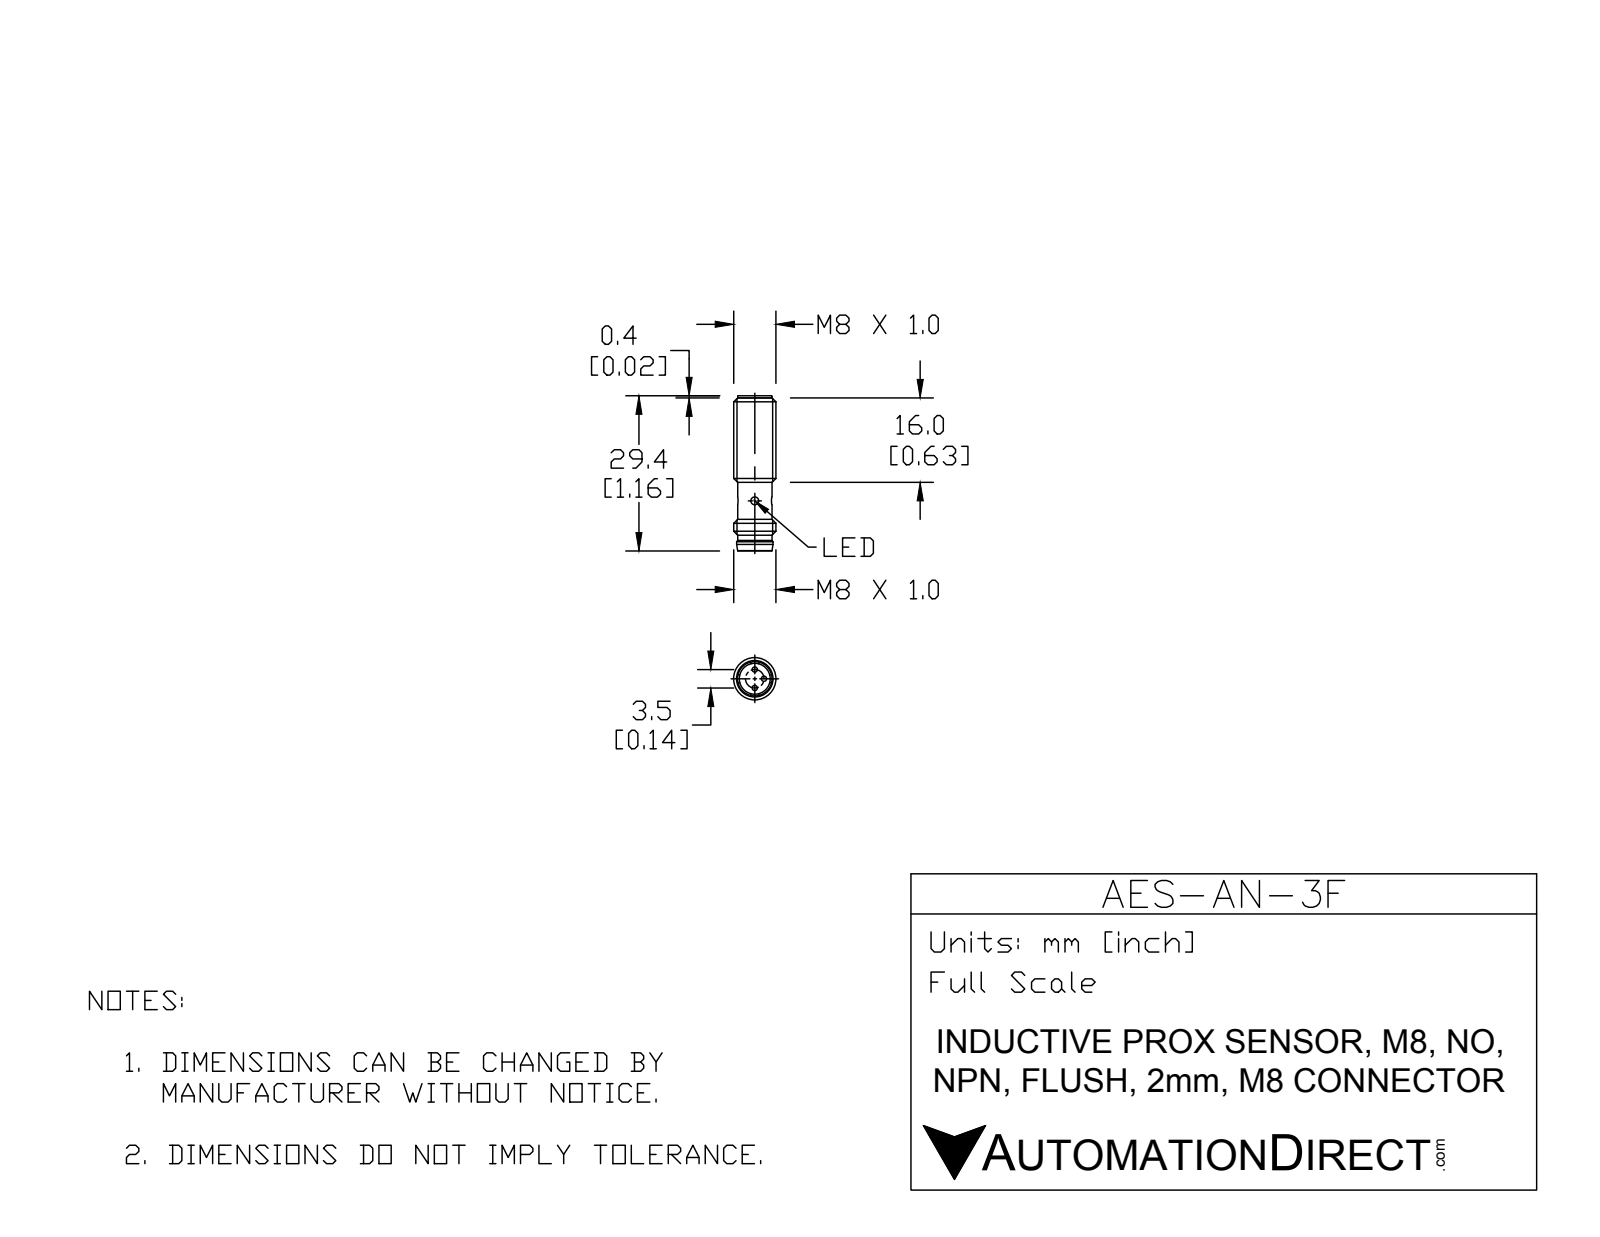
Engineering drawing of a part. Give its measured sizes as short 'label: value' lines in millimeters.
name: AES-AN-3F
written by: SolidWorks 2015 (CONFIG_CONTROL_DESIGN)
unit: mm
bodies: 1 solid, 58 faces (10 planar, 28 cylindrical, 20 other)
size: 29.4 × 8 × 8
volume: 1 157 mm³; area: 928 mm²
holes: 2× ⌀1.5, 1× ⌀5.85
bosses: 3× ⌀1, 1× ⌀8, 1× ⌀6.9, 1× ⌀6.5
face distances: 24.4, 3, 27.4, 5.5, 11, 8, 16.4, 27, 24, 16
